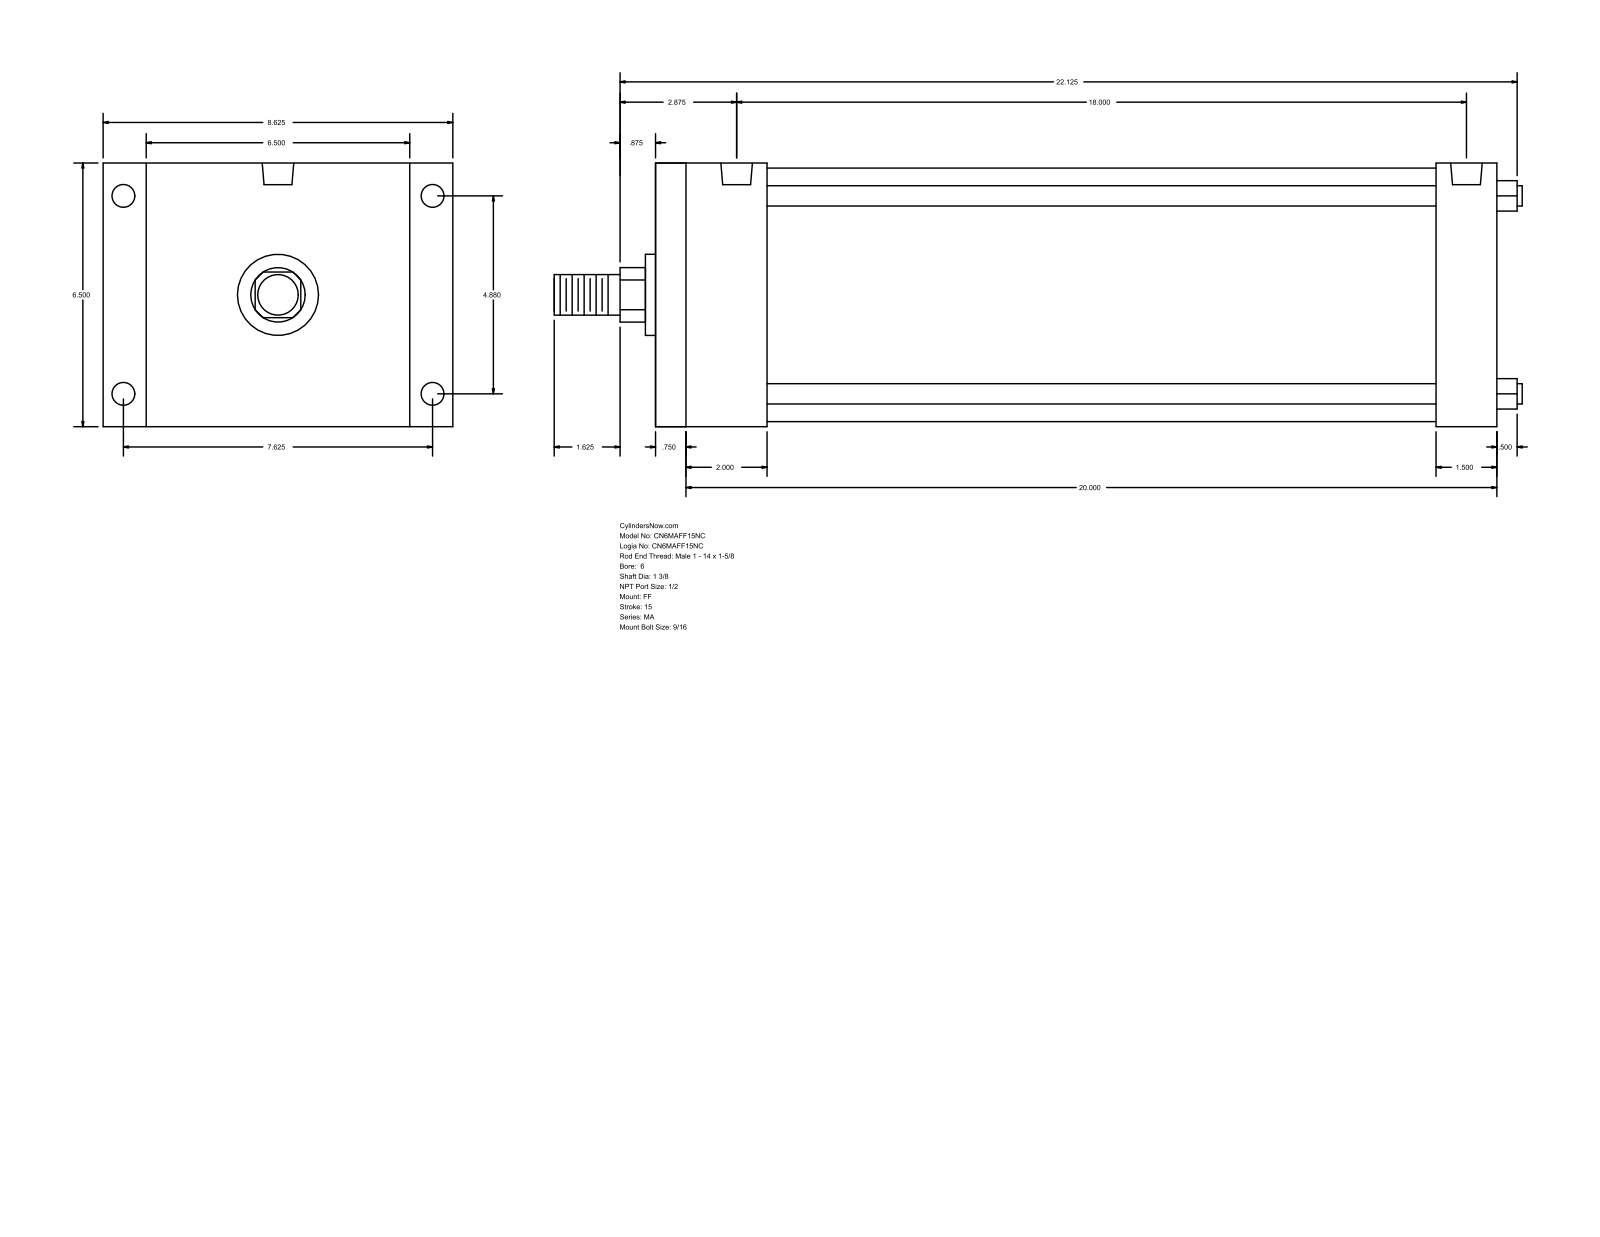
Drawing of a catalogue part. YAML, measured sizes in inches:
part_name: "MA_FF__0600_1.375"
step_written_by: "GSSL Pune (CONFIG_CONTROL_DESIGN)"
units: inches
bodies: {solids: 0, faces: 92, planar: 64, cylindrical: 28, other: 0}
overall_size: [23.875, 8.625, 6.5]
round_holes:
  - {diameter: 0.563, count: 4}
  - {diameter: 0.687, count: 4}
  - {diameter: 0.778, count: 2}
round_bosses_or_shafts:
  - {diameter: 0.5, count: 4}
  - {diameter: 6.25, count: 1}
  - {diameter: 2, count: 1}
  - {diameter: 1.375, count: 1}
  - {diameter: 1, count: 1}
partial_cylinders:
  - {radius: 0.672, count: 1}
face_to_face_distances: [6.5, 20.75, 0.625, 20.125, 2, 18.625, 2.625, 18.125, 19.25, 16.625]
hole_center_spacings: [4.88, 7.625, 9.053, 18.125, 0.125, 18]
